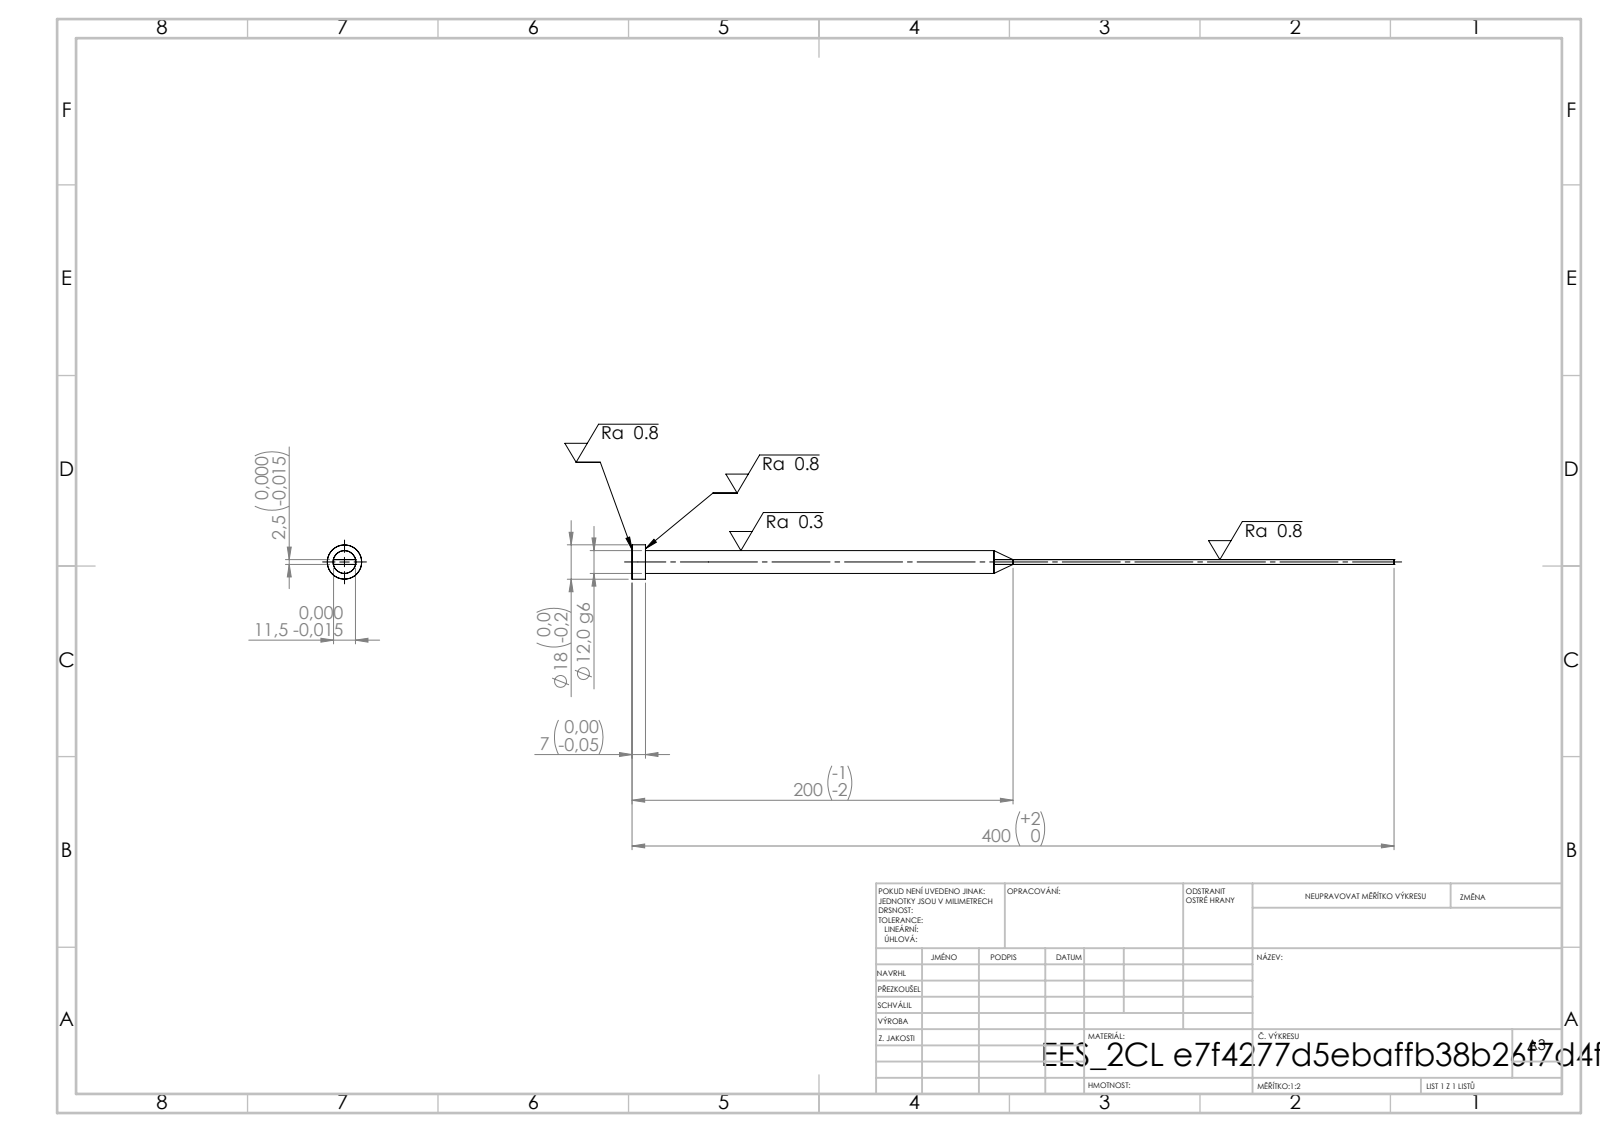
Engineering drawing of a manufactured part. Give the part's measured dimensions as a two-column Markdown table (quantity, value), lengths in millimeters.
| quantity | value |
| --- | --- |
| STEP written by | SolidWorks 2019 (CONFIG_CONTROL_DESIGN) |
| units | millimeters |
| bodies | 1 solid, 15 faces (7 planar, 4 cylindrical, 4 other) |
| overall size | 400 × 18 × 18 |
| volume | 28 908 mm³ |
| surface area | 13 649 mm² |
| round bosses / shafts (diameter × count) | 18 × 1, 12 × 1 |
| main face-to-face distances | 2.5, 11.5, 7, 400, 393 |
